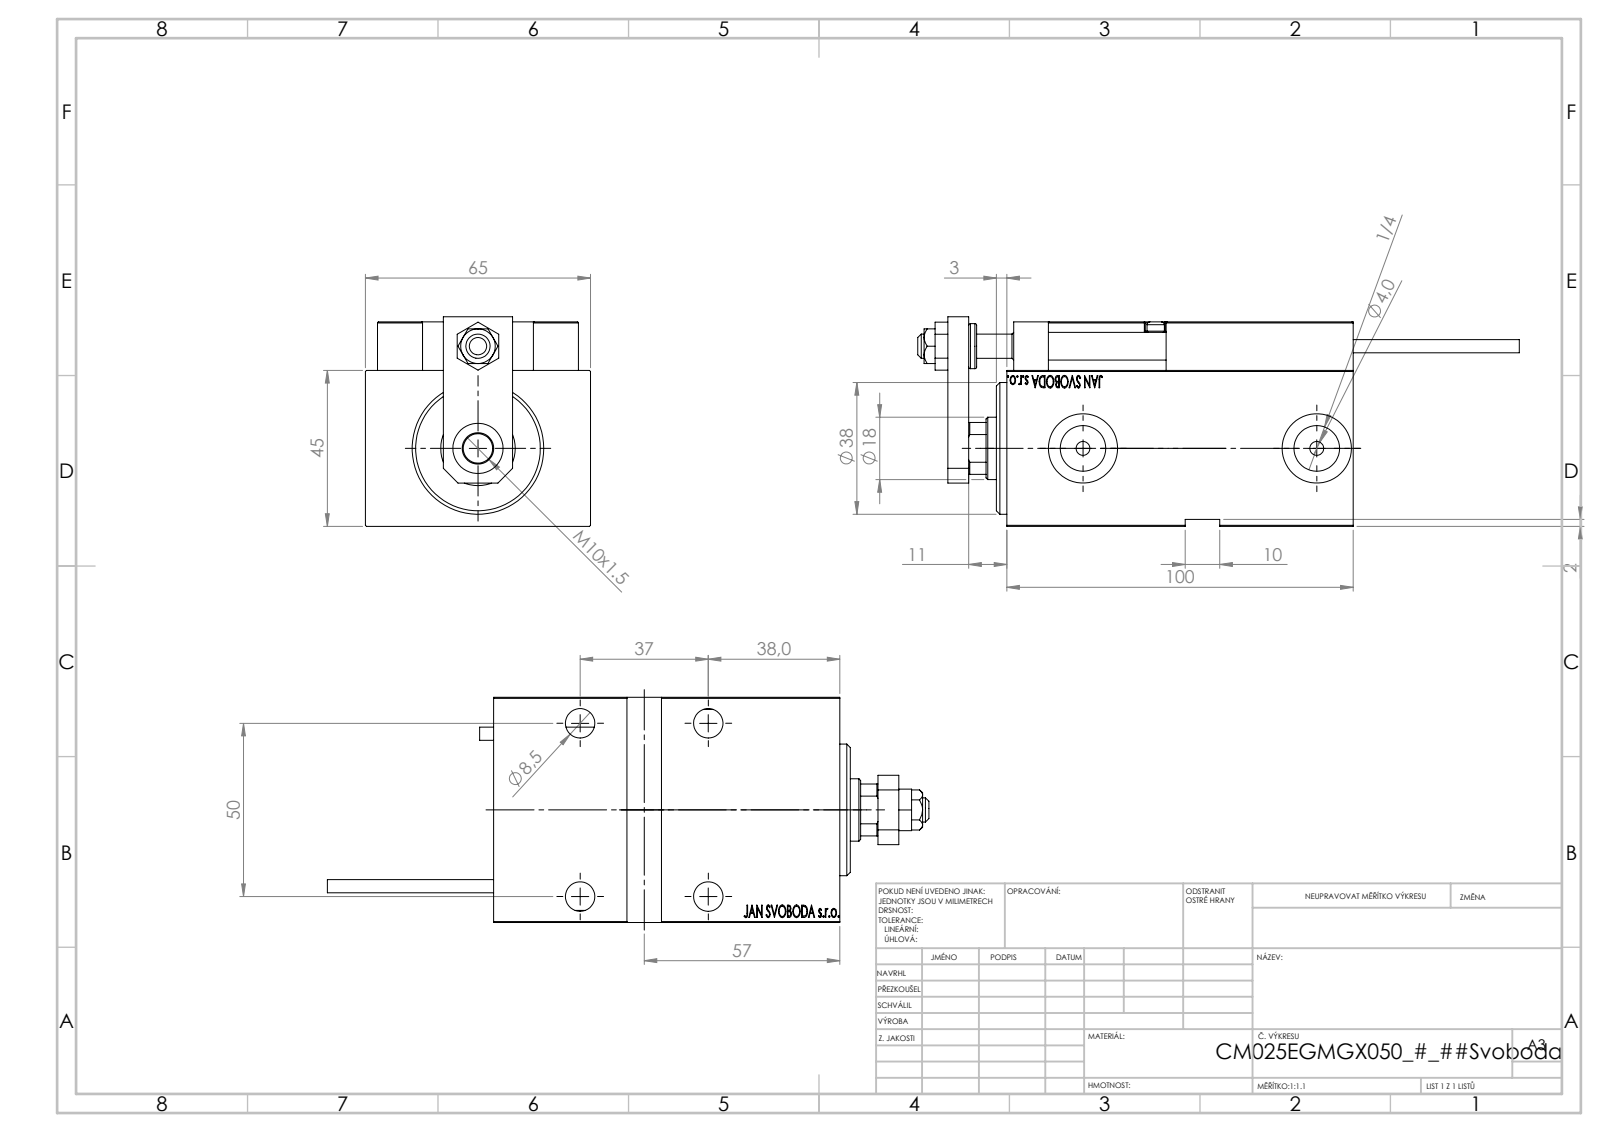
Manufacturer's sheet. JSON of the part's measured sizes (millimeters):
{"part_name": "KONCOVKA; MAGNET; ALLEN BOLT D8; V450CM_E_Body (+7 more)", "step_written_by": "SolidWorks 2019 (CONFIG_CONTROL_DESIGN)", "units": "millimeters", "bodies": {"solids": 24, "faces": 1293, "planar": 570, "cylindrical": 182, "other": 541}, "overall_size": [173.7, 65, 60.5], "volume_mm3": 314176, "surface_area_mm2": 78714, "round_holes": [[4, 6], [8, 5], [8.5, 5], [3.2, 4], [13.5, 4], [5, 2], [13.16, 2], [20, 2], [7, 1], [14.5, 1], [18, 1], [21.5, 1]], "round_bosses_or_shafts": [[5, 2], [3.8, 2], [38, 1], [27, 1], [13, 1], [11, 1]], "partial_cylinders_radius": [[0.3, 30], [3, 2], [8.5, 1]], "face_to_face_distances": [45, 65, 14, 59, 6, 13, 100, 3.5, 111, 10], "hole_center_spacings": [40.31, 11.37, 20, 25, 29.59, 29.69, 34.44, 36.06]}
